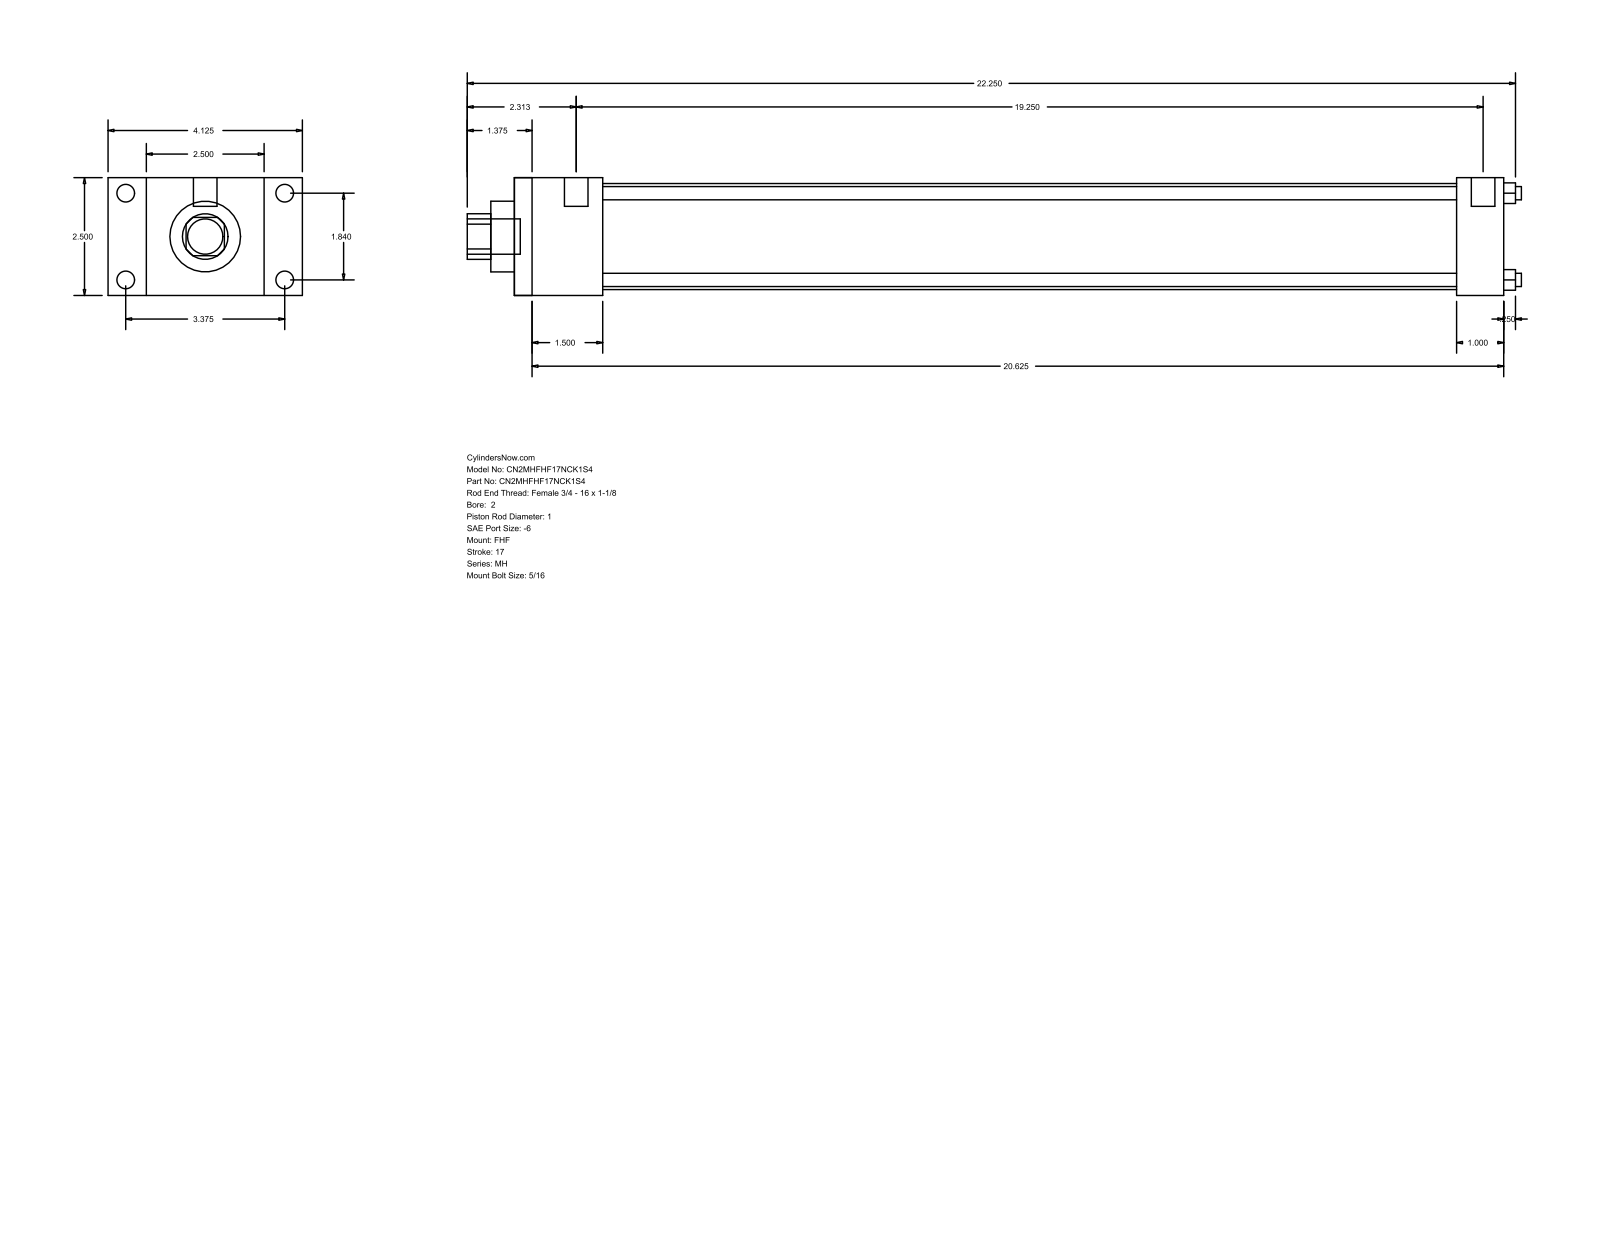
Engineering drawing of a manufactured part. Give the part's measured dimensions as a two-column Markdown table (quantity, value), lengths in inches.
| quantity | value |
| --- | --- |
| part name | MH_FHF__0200_1 |
| STEP written by | GSSL Pune (CONFIG_CONTROL_DESIGN) |
| units | inches |
| bodies | 0 solids, 88 faces (60 planar, 28 cylindrical, 0 other) |
| overall size | 22.375 × 4.125 × 2.5 |
| round holes (diameter × count) | 0.281 × 4, 1 × 1, 1.5 × 1, 2.25 × 1 |
| round bosses / shafts (diameter × count) | 0.375 × 4, 0.219 × 4, 0.5 × 2, 0.75 × 1 |
| partial cylindrical surfaces (radius × count) | 0.484 × 1 |
| main face-to-face distances | 2.5, 21, 1.875, 19.125, 0.813, 3.313, 4.125, 1, 20, 18.125 |
| hole center spacings | 1.301, 1.84, 2.602 |
